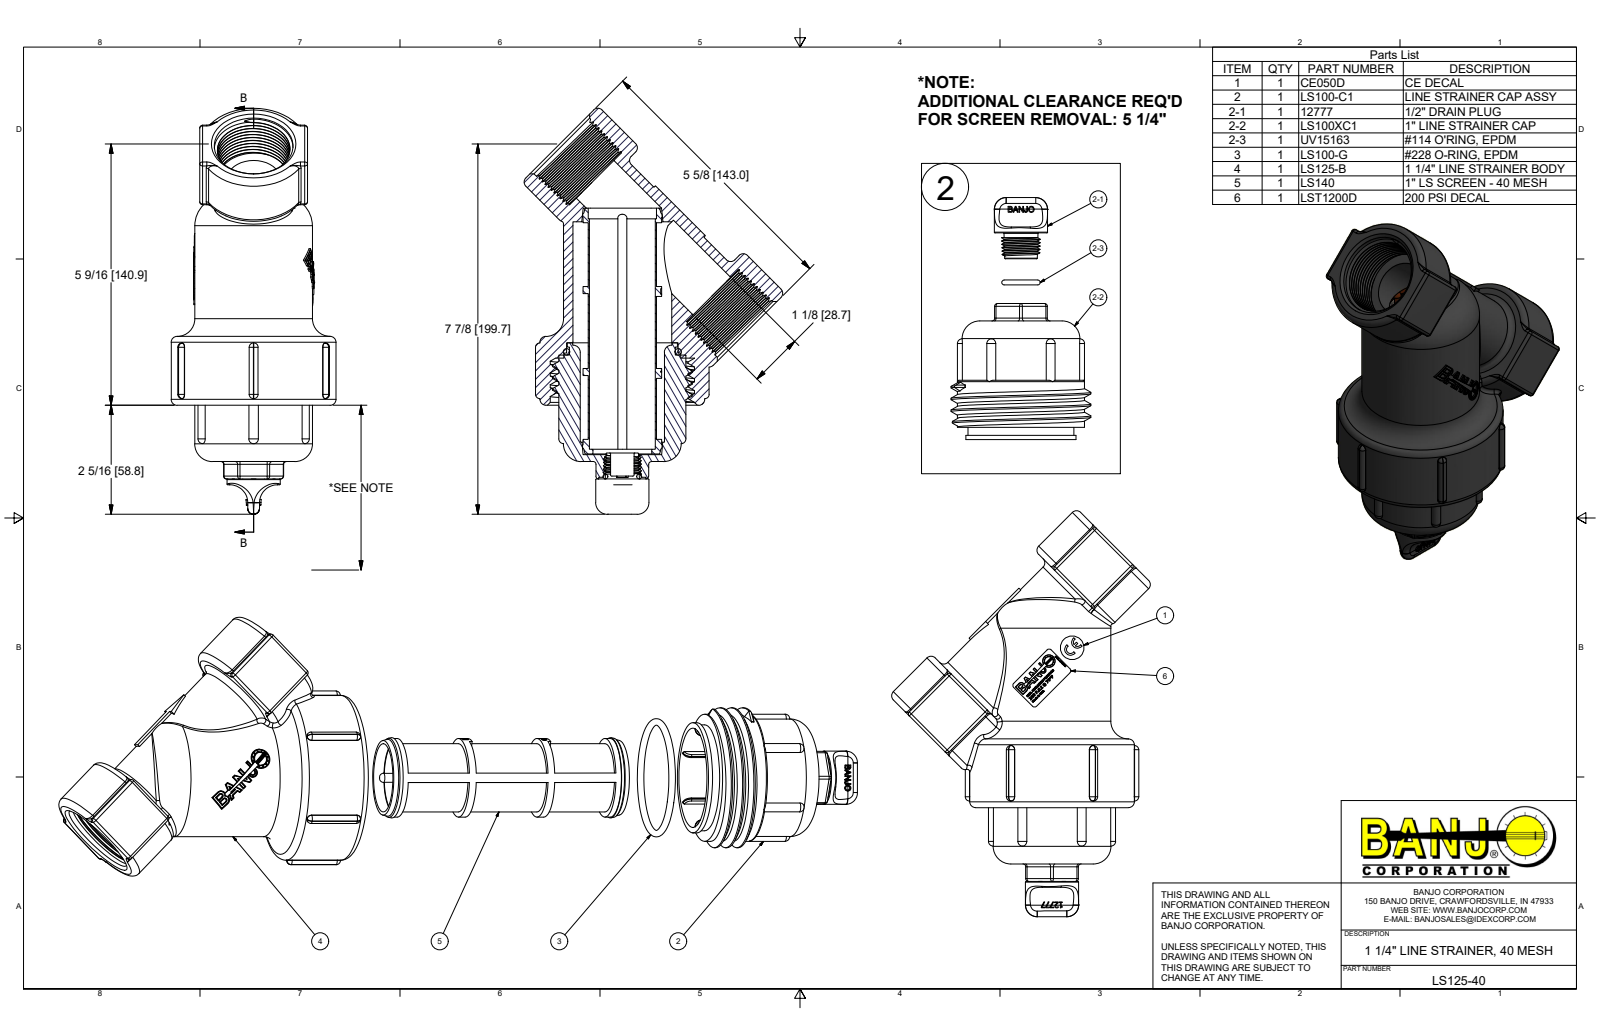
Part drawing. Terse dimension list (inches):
name: LS125-40; LS125-B; LS100-C1; LS100XC1 (+6 more)
written by: Autodesk Inventor 2018 (AUTOMOTIVE_DESIGN)
unit: in
bodies: 8 solids, 2295 faces (1211 planar, 331 cylindrical, 753 other)
size: 34.216 × 34.216 × 3.5
volume: 24.13 in³; area: 1 353 in²
holes: 2× ⌀1.13, 1× ⌀0.181, 1× ⌀0.257, 1× ⌀0.272, 1× ⌀0.385, 1× ⌀0.5, 1× ⌀1.005, 1× ⌀1.25, 1× ⌀1.4, 1× ⌀2.1, 1× ⌀2.11, 1× ⌀2.371
bosses: 1× ⌀3.5, 1× ⌀2.971, 1× ⌀2.7, 1× ⌀2.5, 1× ⌀2.34, 1× ⌀2.25, 1× ⌀1.67, 1× ⌀1.45
rounds: 54× R0.06, 39× R0.09, 19× R0.03, 9× R0.1, 6× R0.15, 2× R0.026, 2× R0.033, 2× R0.039
face distances: 0.2, 2.29, 2.05, 0.325, 1.26, 0.065, 1.06, 4.569, 2.375, 2.115
hole spacings: 0.919
